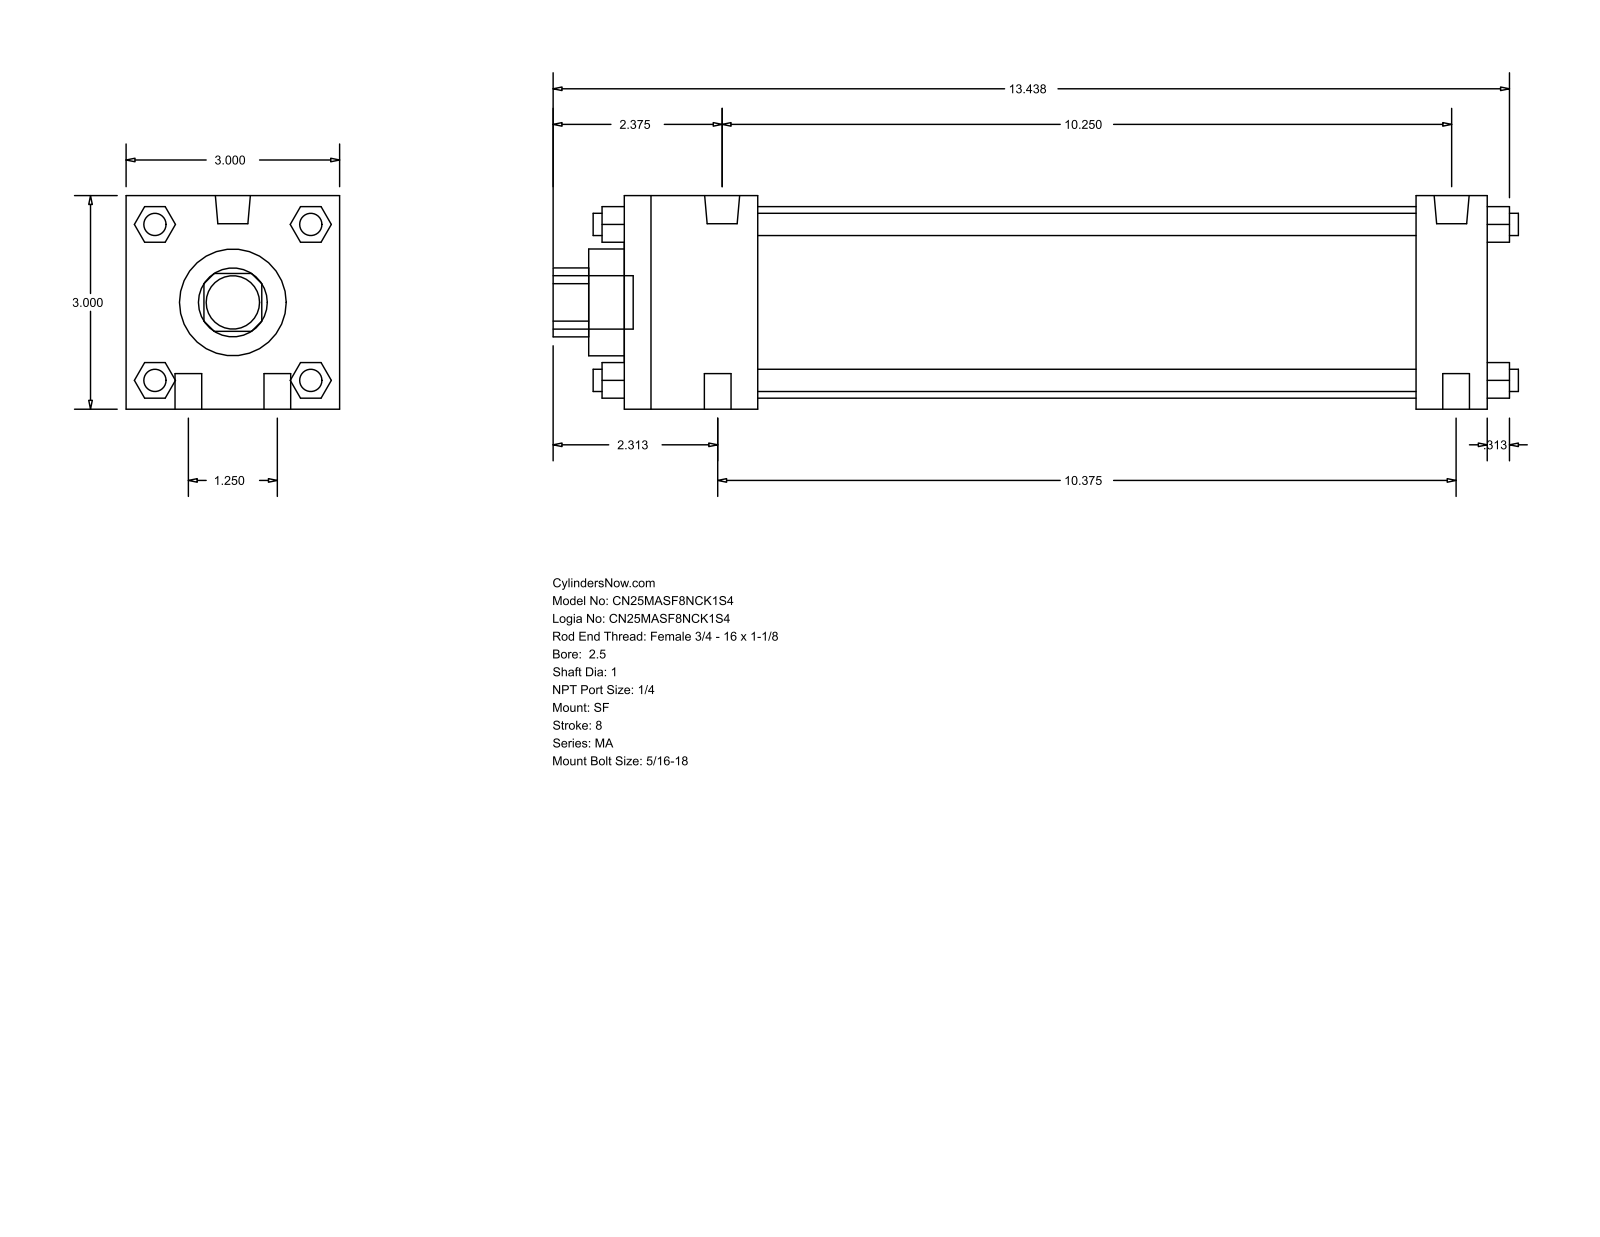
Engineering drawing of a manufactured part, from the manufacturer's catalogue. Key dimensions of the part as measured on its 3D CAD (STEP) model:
Part name (STEP PRODUCT): MA_SF__0250_1
STEP written by: GSSL Pune (CONFIG_CONTROL_DESIGN)
Units: millimetres
Bodies: 0 solids, 124 faces (94 planar, 30 cylindrical, 0 other)
Overall size (bounding box): 344.49 × 76.2 × 76.2
Round holes (diameter × count): ⌀25.4 ×1, ⌀38.1 ×1, ⌀68.33 ×1
Round bosses / shafts (diameter × count): ⌀7.94 ×6, ⌀9.53 ×4, ⌀12.49 ×2, ⌀19.05 ×1
Partial cylindrical surfaces — rounded edges, fillets, slot ends (radius × count): R12.29 ×1
Main face-to-face distances: 76.2, 307.98, 12.7, 25.4, 282.58, 47.63, 234.95, 260.35, 27.81, 48.17
